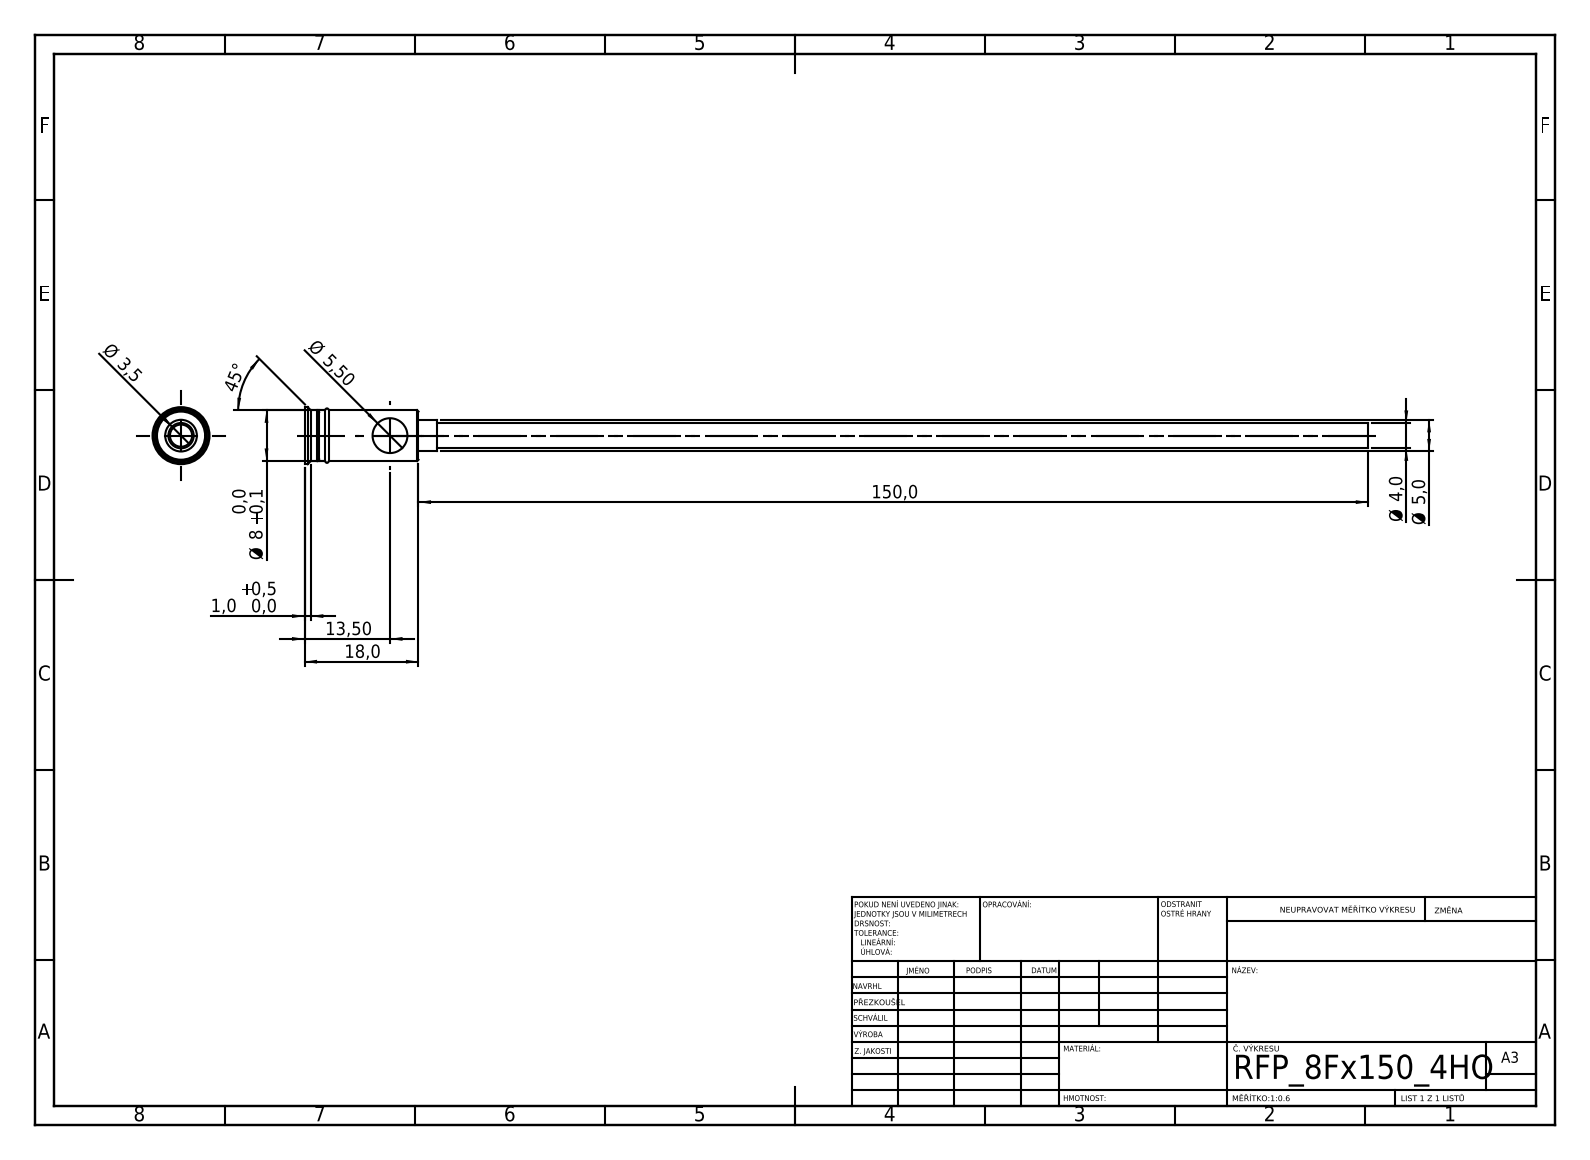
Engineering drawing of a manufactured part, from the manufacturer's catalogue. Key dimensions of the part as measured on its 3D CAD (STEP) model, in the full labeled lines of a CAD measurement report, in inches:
STEP written by: SolidWorks 2019 (CONFIG_CONTROL_DESIGN)
Units: inches
Bodies: 1 solid, 44 faces (20 planar, 16 cylindrical, 8 other)
Overall size (bounding box): 6.614 × 0.354 × 0.354
Volume: 0.071 in³ · Surface area: 6.557 in²
Round holes (diameter × count): ⌀0.138 ×1, ⌀0.217 ×1
Round bosses / shafts (diameter × count): ⌀0.354 ×1, ⌀0.315 ×1, ⌀0.197 ×1, ⌀0.157 ×1
Main face-to-face distances: 0.709, 0.134, 0.63, 0.079, 0.618, 0.091, 0.118, 0.736, 0.748, 0.827
